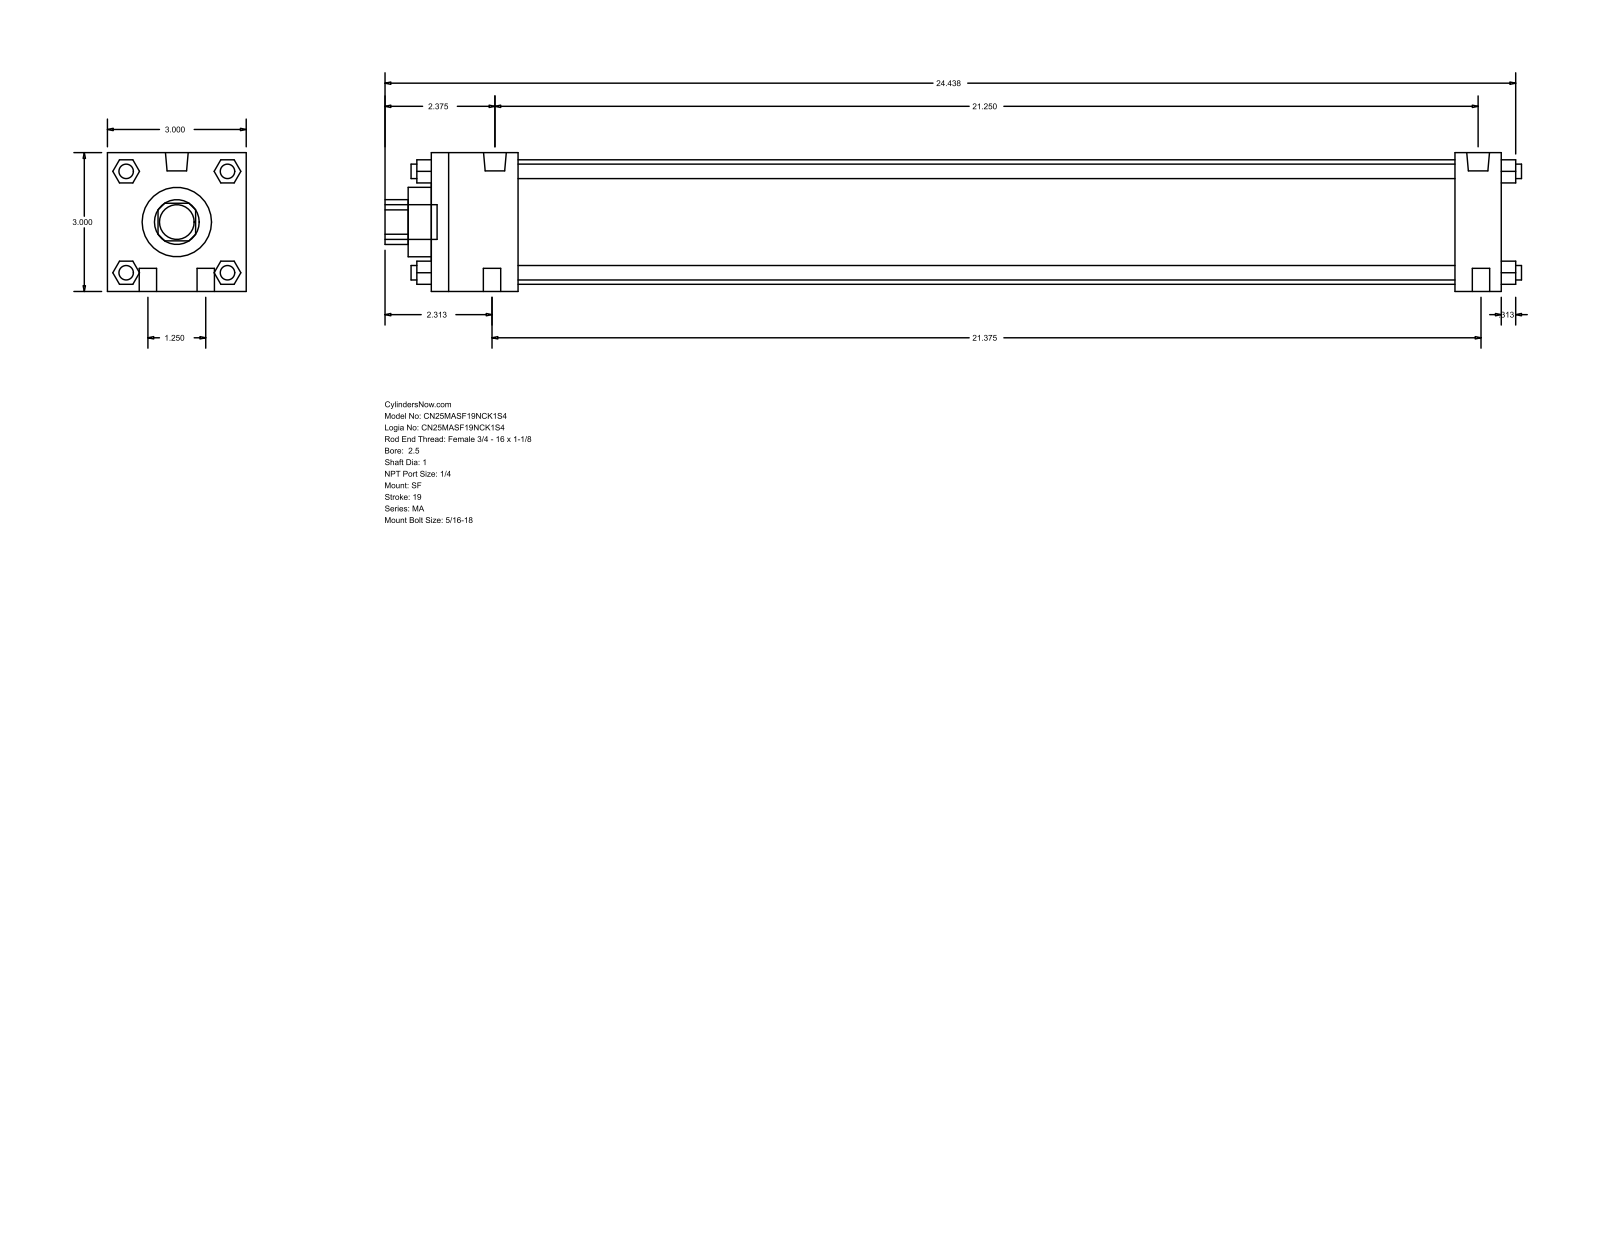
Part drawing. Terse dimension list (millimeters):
name: MA_SF__0250_1
written by: GSSL Pune (CONFIG_CONTROL_DESIGN)
unit: mm
bodies: 0 solids, 124 faces (94 planar, 30 cylindrical, 0 other)
size: 623.89 × 76.2 × 76.2
holes: 1× ⌀25.4, 1× ⌀38.1, 1× ⌀68.33
bosses: 6× ⌀7.94, 4× ⌀9.53, 2× ⌀12.49, 1× ⌀19.05
rounds: 1× R12.29
face distances: 76.2, 587.37, 12.7, 561.98, 25.39, 47.63, 514.35, 539.74, 27.81, 48.17
